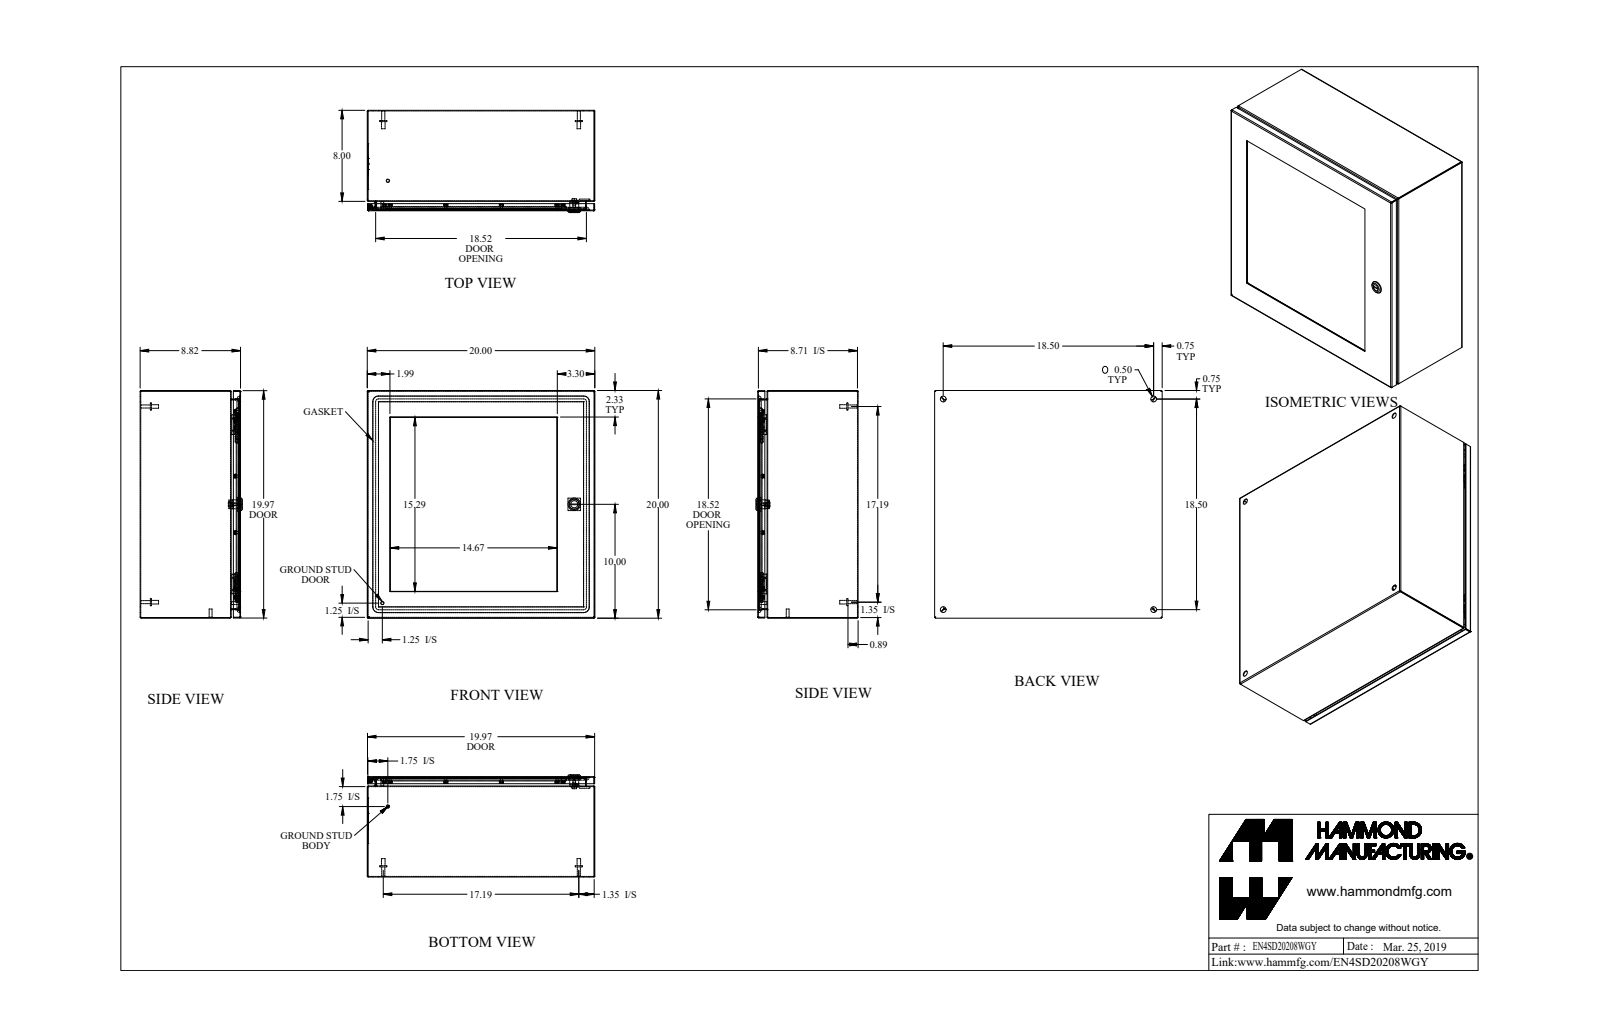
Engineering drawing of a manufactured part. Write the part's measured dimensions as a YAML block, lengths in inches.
part_name: "EN4SD20208WGY_Default"
step_written_by: "SolidWorks 2019 (CONFIG_CONTROL_DESIGN)"
units: inches
bodies: {solids: 62, faces: 1265, planar: 628, cylindrical: 389, other: 248}
overall_size: [20, 20, 8.982]
volume: 152
surface_area: 3619
round_holes:
  - {diameter: 0.13, count: 16}
  - {diameter: 0.25, count: 16}
  - {diameter: 0.5, count: 4}
  - {diameter: 0.172, count: 1}
  - {diameter: 0.232, count: 1}
  - {diameter: 0.24, count: 1}
  - {diameter: 0.242, count: 1}
  - {diameter: 0.625, count: 1}
  - {diameter: 0.785, count: 1}
round_bosses_or_shafts:
  - {diameter: 0.226, count: 17}
  - {diameter: 0.368, count: 16}
  - {diameter: 0.164, count: 16}
  - {diameter: 0.625, count: 4}
  - {diameter: 0.313, count: 4}
  - {diameter: 0.27, count: 4}
  - {diameter: 0.281, count: 2}
  - {diameter: 0.25, count: 2}
partial_cylinders:
  - {radius: 0.029, count: 21}
  - {radius: 0.086, count: 21}
  - {radius: 0.25, count: 16}
  - {radius: 0.125, count: 10}
  - {radius: 19, count: 8}
  - {radius: 0.006, count: 4}
  - {radius: 0.016, count: 4}
  - {radius: 0.062, count: 4}
face_to_face_distances: [0.057, 19.943, 8.765, 8.708, 19.886, 20, 0.25, 8.458, 8.515, 0.307]
hole_center_spacings: [9.78, 16.333, 4.889, 4.89, 4.89, 4.891, 10.324, 16.471]
